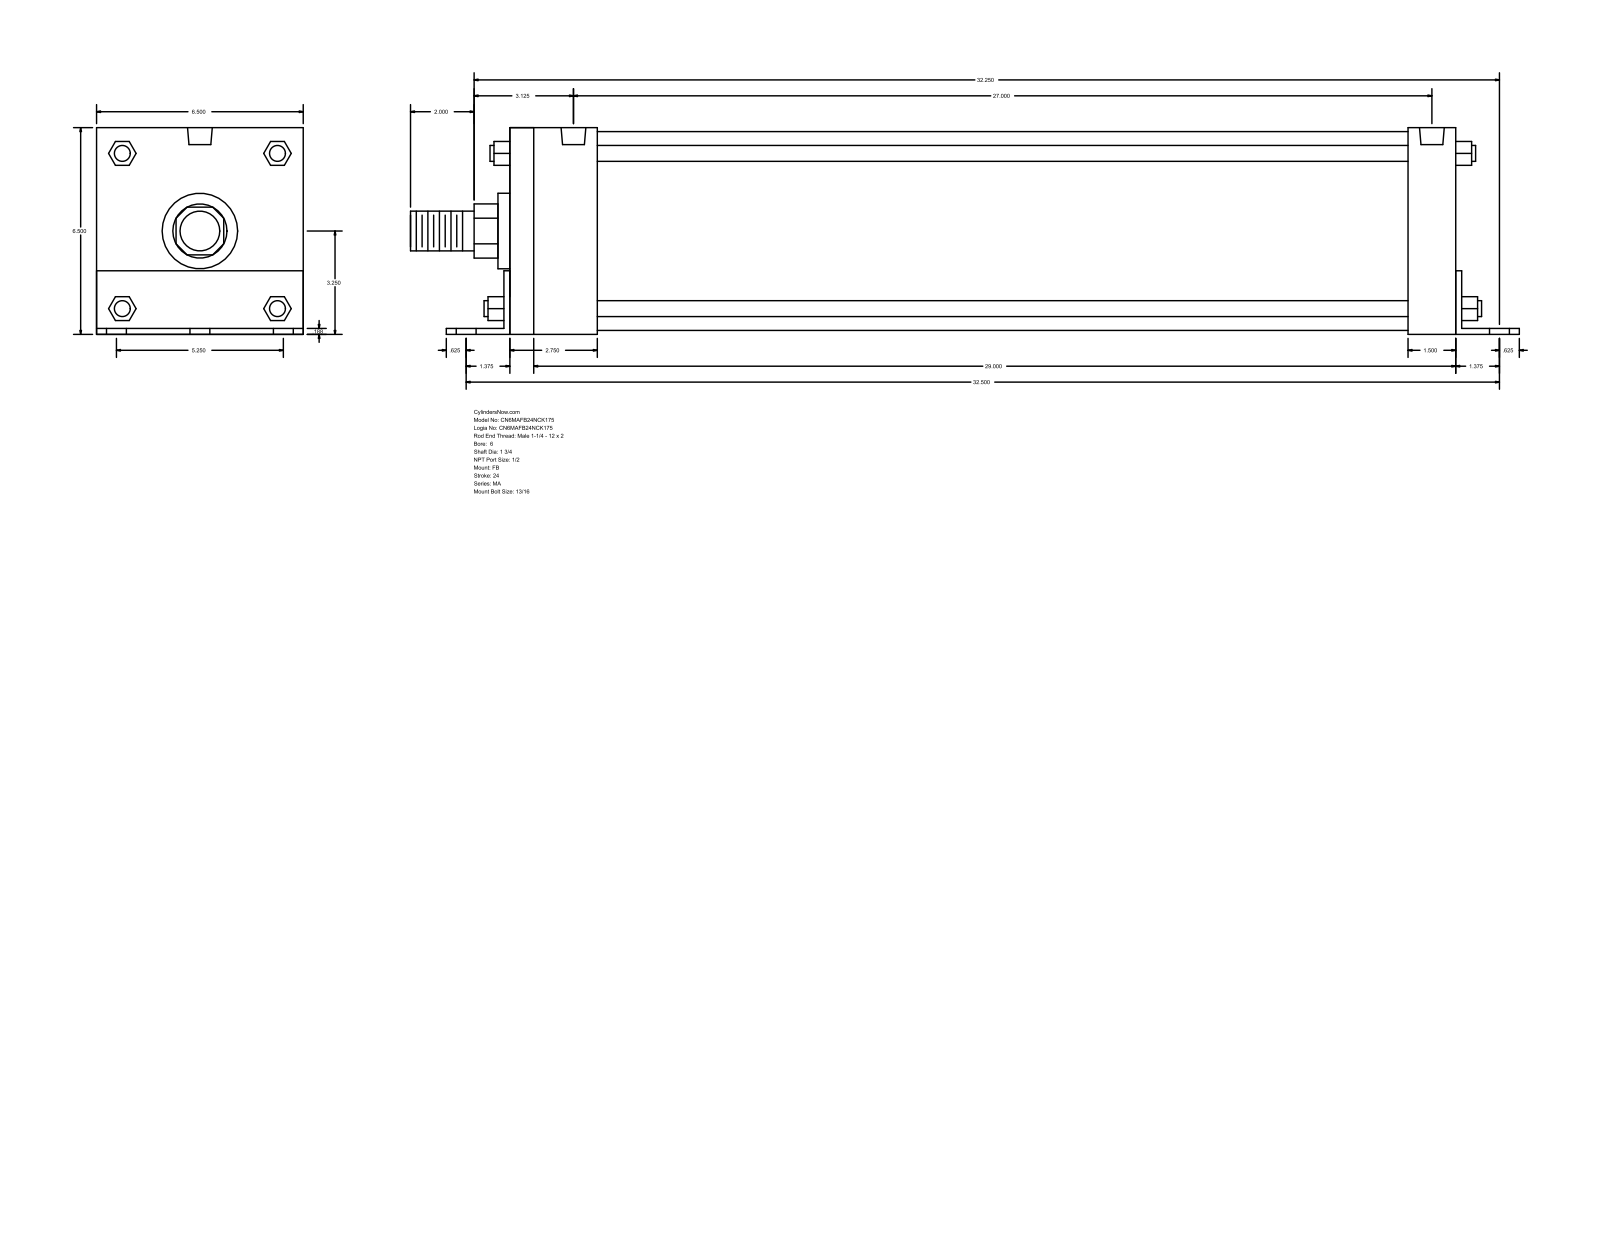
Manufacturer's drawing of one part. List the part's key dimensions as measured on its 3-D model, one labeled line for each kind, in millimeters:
Part name (STEP PRODUCT): MA_FB__0600_1.75
STEP written by: GSSL Pune (CONFIG_CONTROL_DESIGN)
Units: millimetres
Bodies: 0 solids, 140 faces (105 planar, 35 cylindrical, 0 other)
Overall size (bounding box): 885.83 × 165.15 × 165.1
Round holes (diameter × count): ⌀20.64 ×6, ⌀17.46 ×4, ⌀19.77 ×2
Round bosses / shafts (diameter × count): ⌀12.7 ×4, ⌀158.75 ×1, ⌀60.33 ×1, ⌀44.45 ×1, ⌀31.75 ×1
Partial cylindrical surfaces — rounded edges, fillets, slot ends (radius × count): R21.63 ×1, R32.05 ×1
Main face-to-face distances: 165.1, 4.76, 755.66, 165.15, 760.42, 4.71, 160.39, 765.18, 69.85, 74.61
Hole centre spacings: 66.67, 828.19, 825.5, 85.78, 108.6, 133.34, 685.79, 742.77
